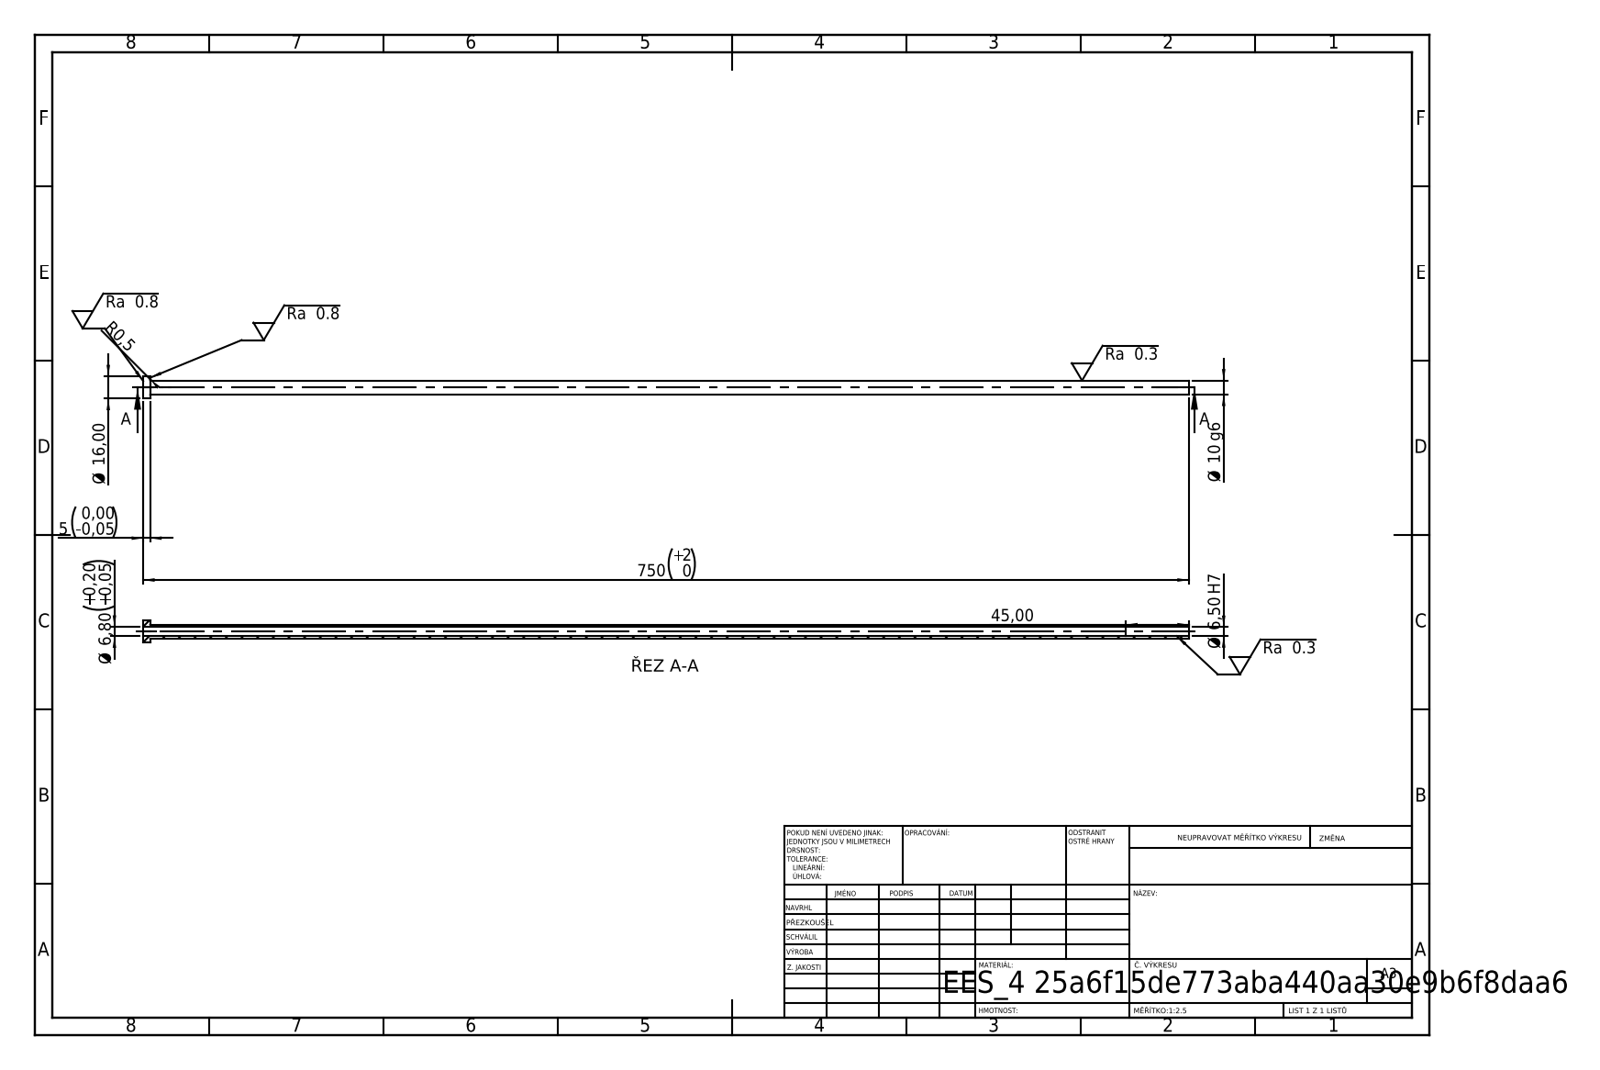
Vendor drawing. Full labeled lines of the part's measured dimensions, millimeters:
STEP written by: SolidWorks 2019 (CONFIG_CONTROL_DESIGN)
Units: millimetres
Bodies: 1 solid, 14 faces (4 planar, 8 cylindrical, 2 other)
Overall size (bounding box): 750 × 16 × 16
Volume: 32 423 mm³ · Surface area: 39 965 mm²
Round holes (diameter × count): ⌀6.5 ×1, ⌀6.8 ×1
Round bosses / shafts (diameter × count): ⌀16 ×1, ⌀10 ×1
Main face-to-face distances: 5, 750, 745, 705, 700, 45
